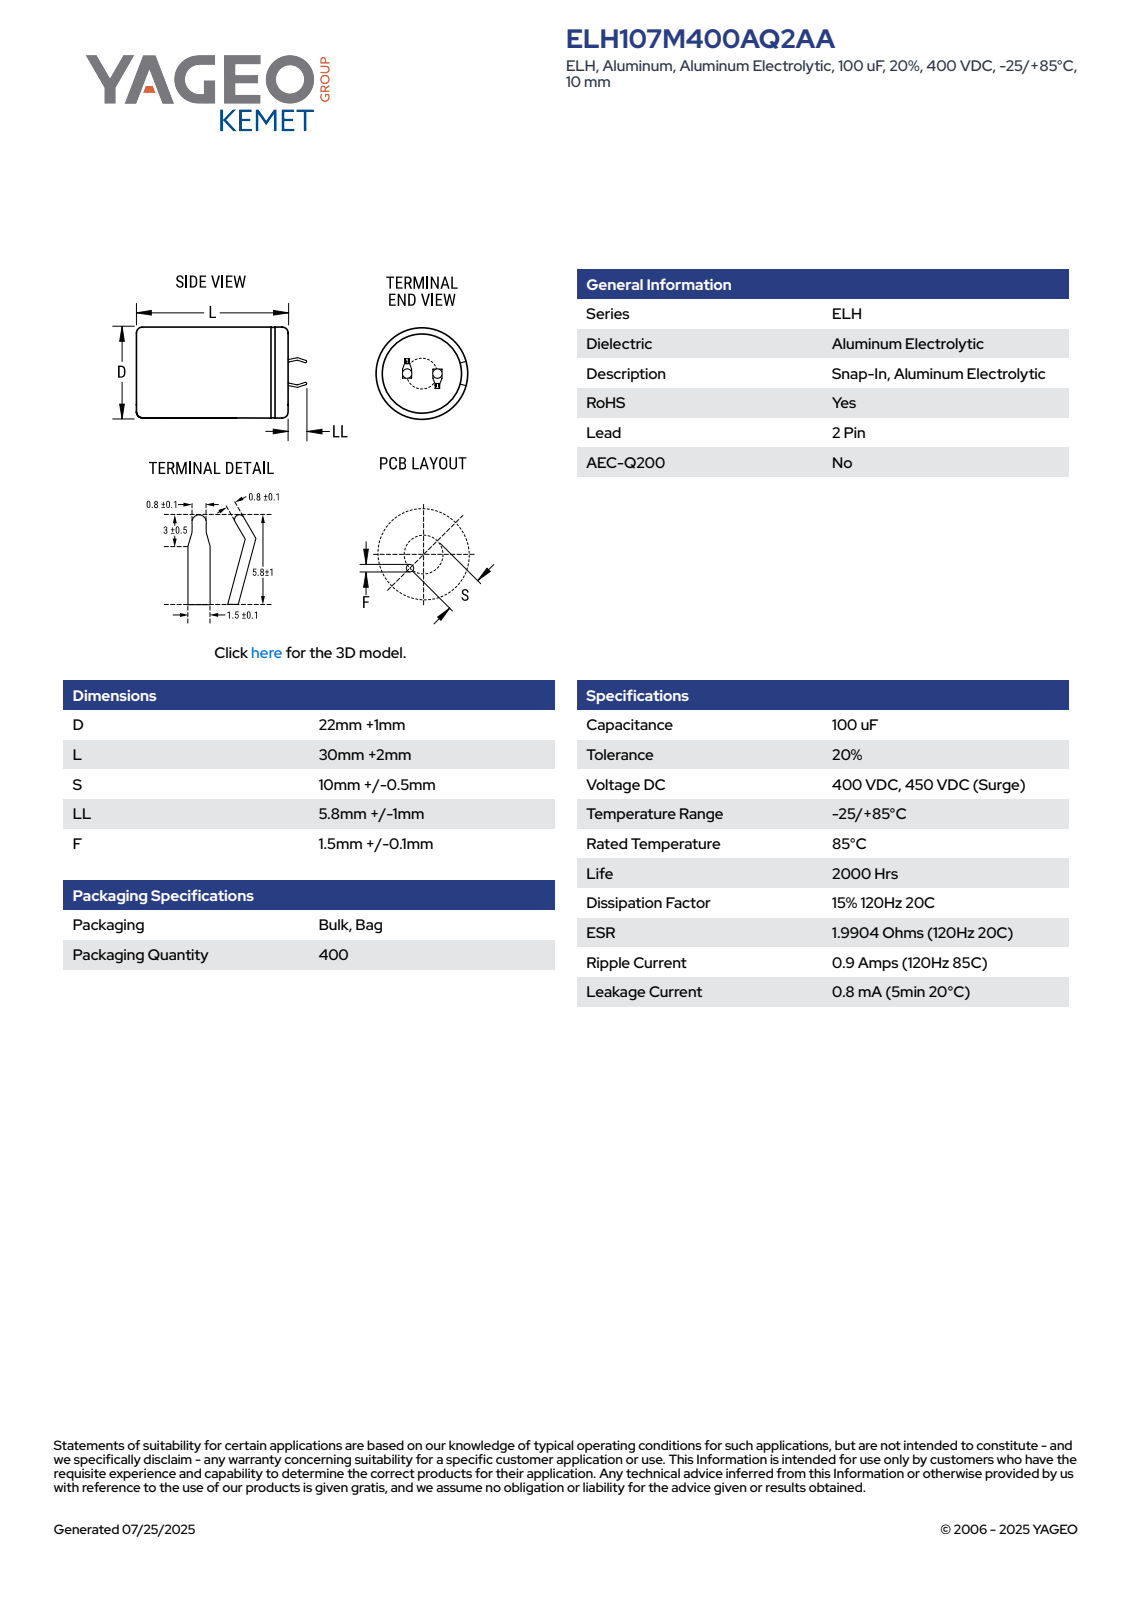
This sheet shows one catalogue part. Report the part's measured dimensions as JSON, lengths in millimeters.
{"part_name": "CARS_K2P_22X30_D23L32S10LL6.8F1.6", "step_written_by": "SolidWorks 2014 (AUTOMOTIVE_DESIGN)", "units": "millimeters", "bodies": {"solids": 1, "faces": 100, "planar": 52, "cylindrical": 9, "other": 39}, "overall_size": [38.79, 23, 23], "volume_mm3": 13165, "surface_area_mm2": 3168, "round_holes": [[20.35, 1]], "round_bosses_or_shafts": [[23, 1]], "partial_cylinders_radius": [[11.49, 1]], "face_to_face_distances": [31.99, 0.6, 32.49, 0.5, 7.08, 7.63, 0.75, 1.35, 7.68, 6.48]}
